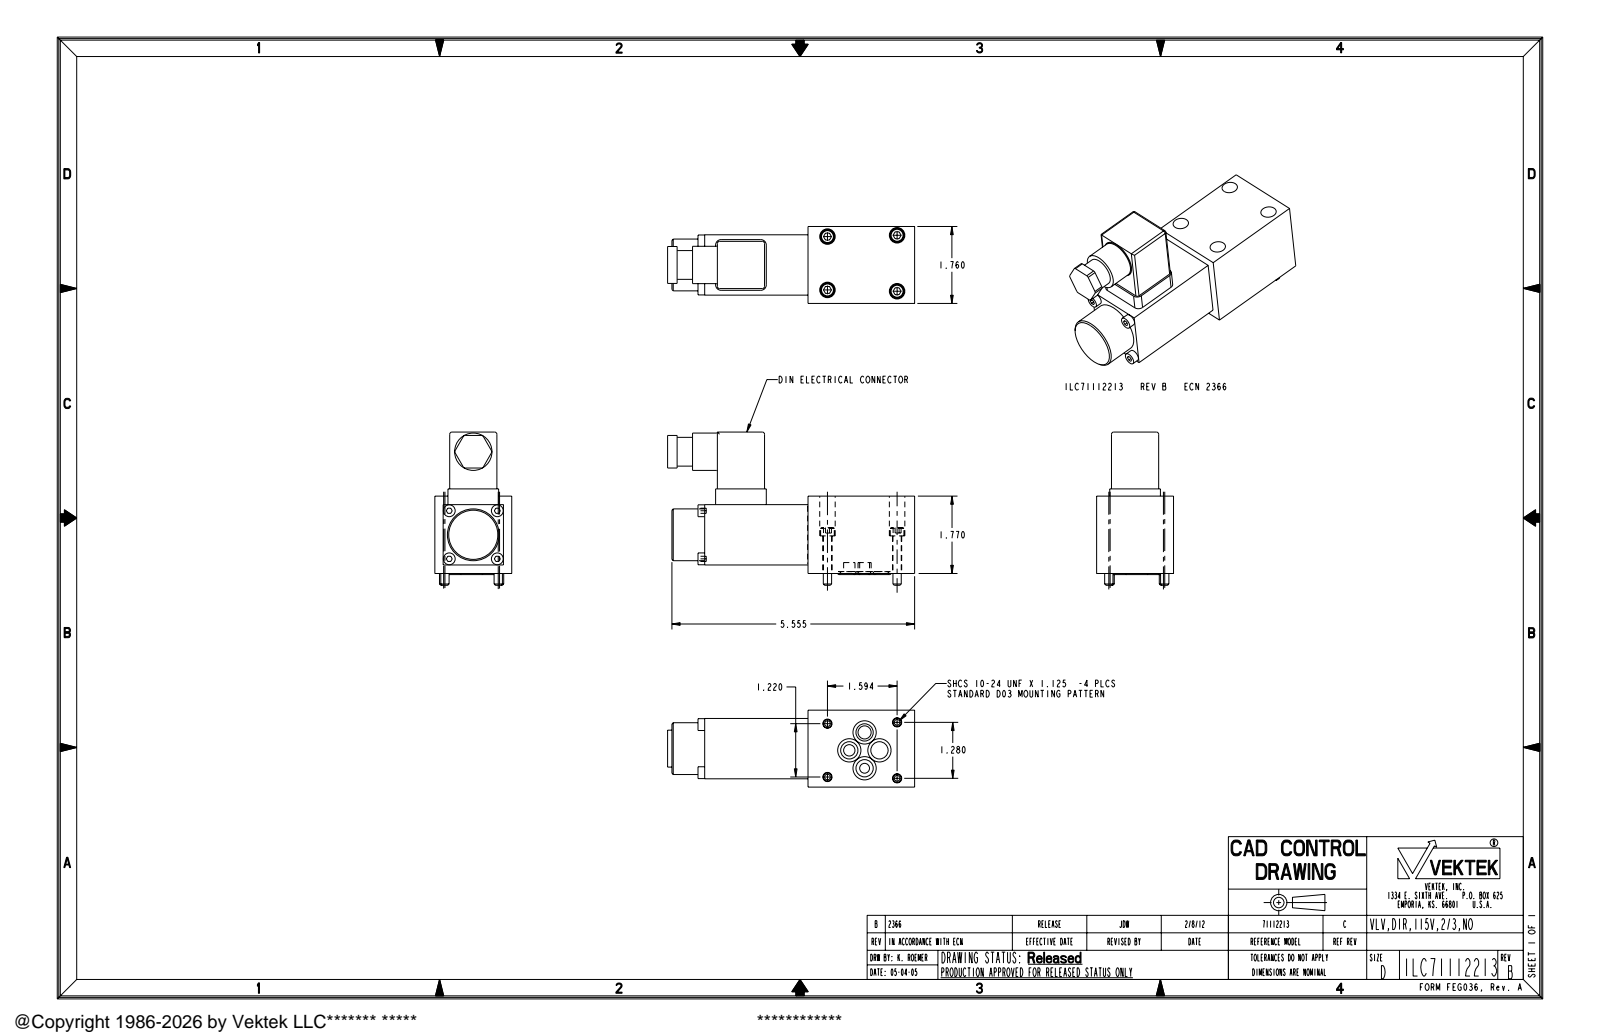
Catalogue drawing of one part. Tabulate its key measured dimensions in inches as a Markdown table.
| quantity | value |
| --- | --- |
| part name | ILC71112213 |
| STEP written by | PRO/ENGINEER BY PARAMETRIC TECHNOLOGY CORPORATION, 2007460 (AUTOMOTIVE_DESIGN_CC2) |
| units | inches |
| bodies | 1 solid, 285 faces (162 planar, 93 cylindrical, 30 other) |
| overall size | 5.654 × 3.505 × 1.76 |
| volume | 15.07 in³ |
| surface area | 63.96 in² |
| round holes (diameter × count) | 0.21 × 4, 0.354 × 4, 0.49 × 4, 0.225 × 1, 0.26 × 1, 0.3 × 1, 0.45 × 1, 1.315 × 1 |
| round bosses / shafts (diameter × count) | 0.313 × 4, 0.271 × 4, 0.19 × 4, 1.265 × 1, 1.185 × 1, 0.854 × 1, 0.658 × 1, 0.15 × 1 |
| partial cylindrical surfaces (radius × count) | 0.05 × 13, 0.015 × 4, 0.04 × 4, 0.125 × 4 |
| main face-to-face distances | 0.19, 1.57, 1.575, 0.195, 1.38, 1.76, 1.77, 0.15, 1.42, 0.34 |
| hole center spacings | 0.533, 0.539, 0.757, 0.779, 0.788, 0.873, 1.268, 1.287 |
